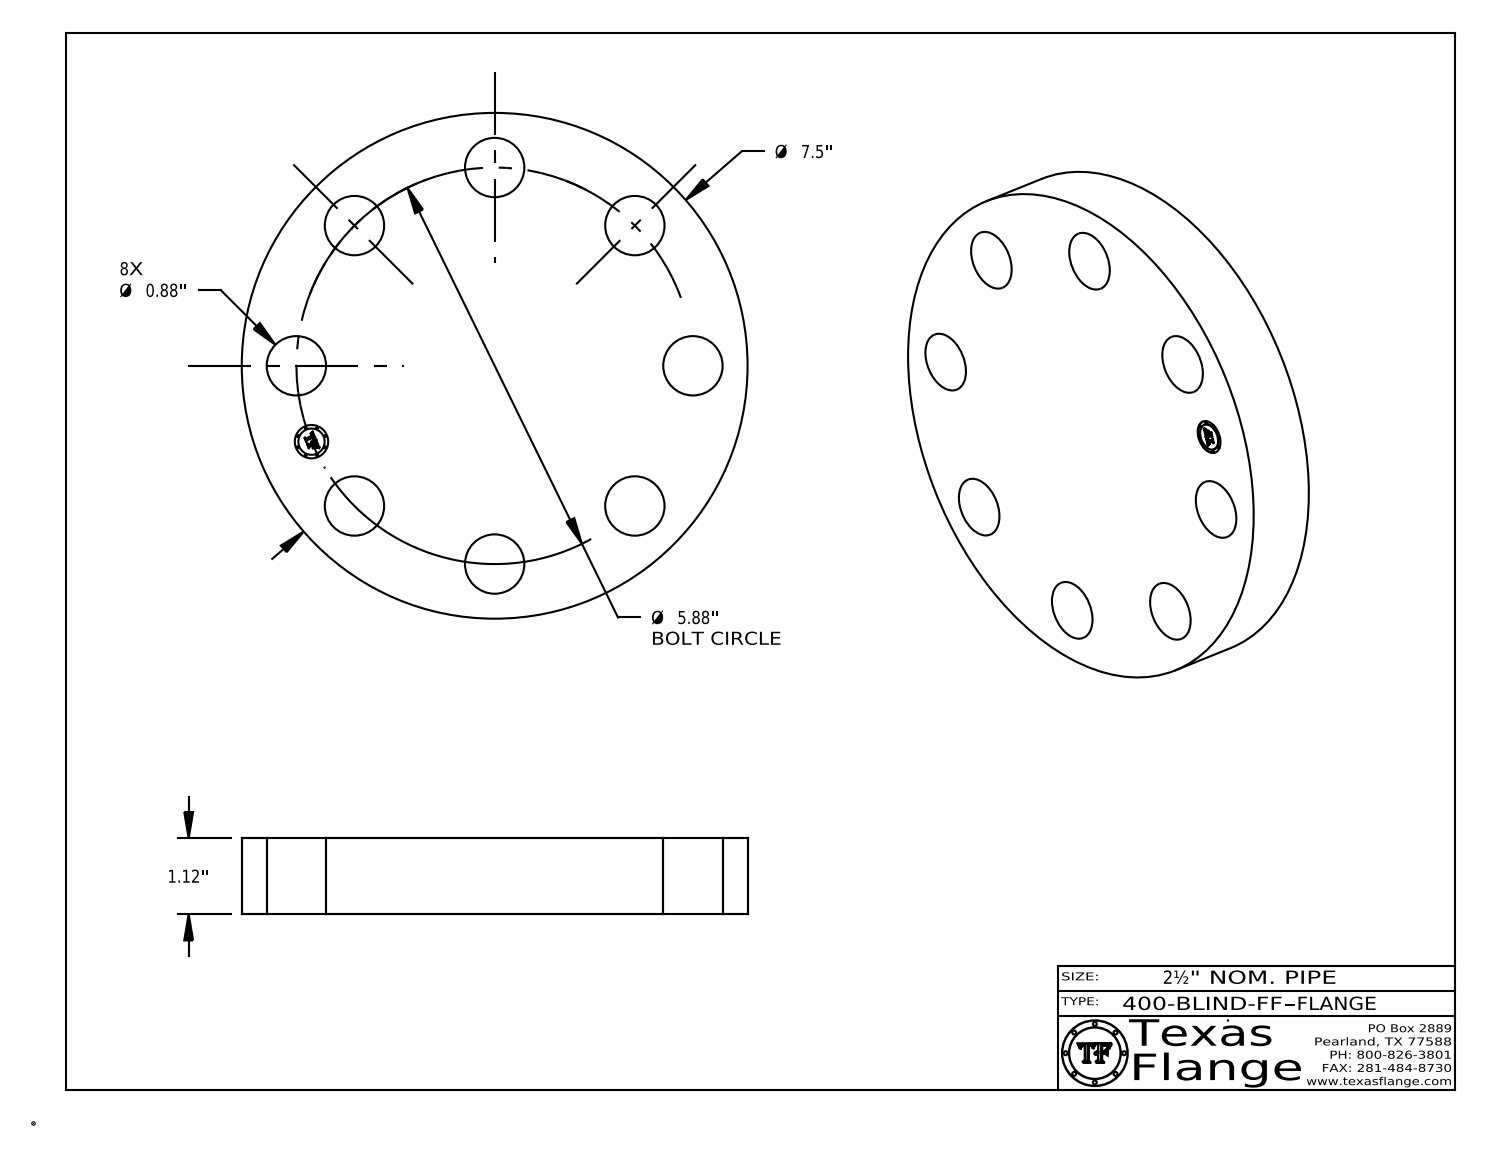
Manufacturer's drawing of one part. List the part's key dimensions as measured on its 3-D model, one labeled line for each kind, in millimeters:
Part name (STEP PRODUCT): 400-BLIND-FF
STEP written by: CATIA V5 STEP AP214 (AUTOMOTIVE_DESIGN)
Units: millimetres
Bodies: 1 solid, 405 faces (367 planar, 38 cylindrical, 0 other)
Overall size (bounding box): 190.5 × 190.5 × 28.4
Volume: 721 500 mm³ · Surface area: 83 810 mm²
Round holes (diameter × count): ⌀22.4 ×8, ⌀12.6 ×1
Round bosses / shafts (diameter × count): ⌀0.8 ×8, ⌀190.5 ×1, ⌀9.9 ×1
Main face-to-face distances: 28.4, 0.4, 28.1, 3.8, 3.7, 0.7, 2.4, 3.1, 0.6, 1.9
Hole centre spacings: 57.2, 138, 105.6, 105.6, 83, 149.4, 149.4, 29.1
